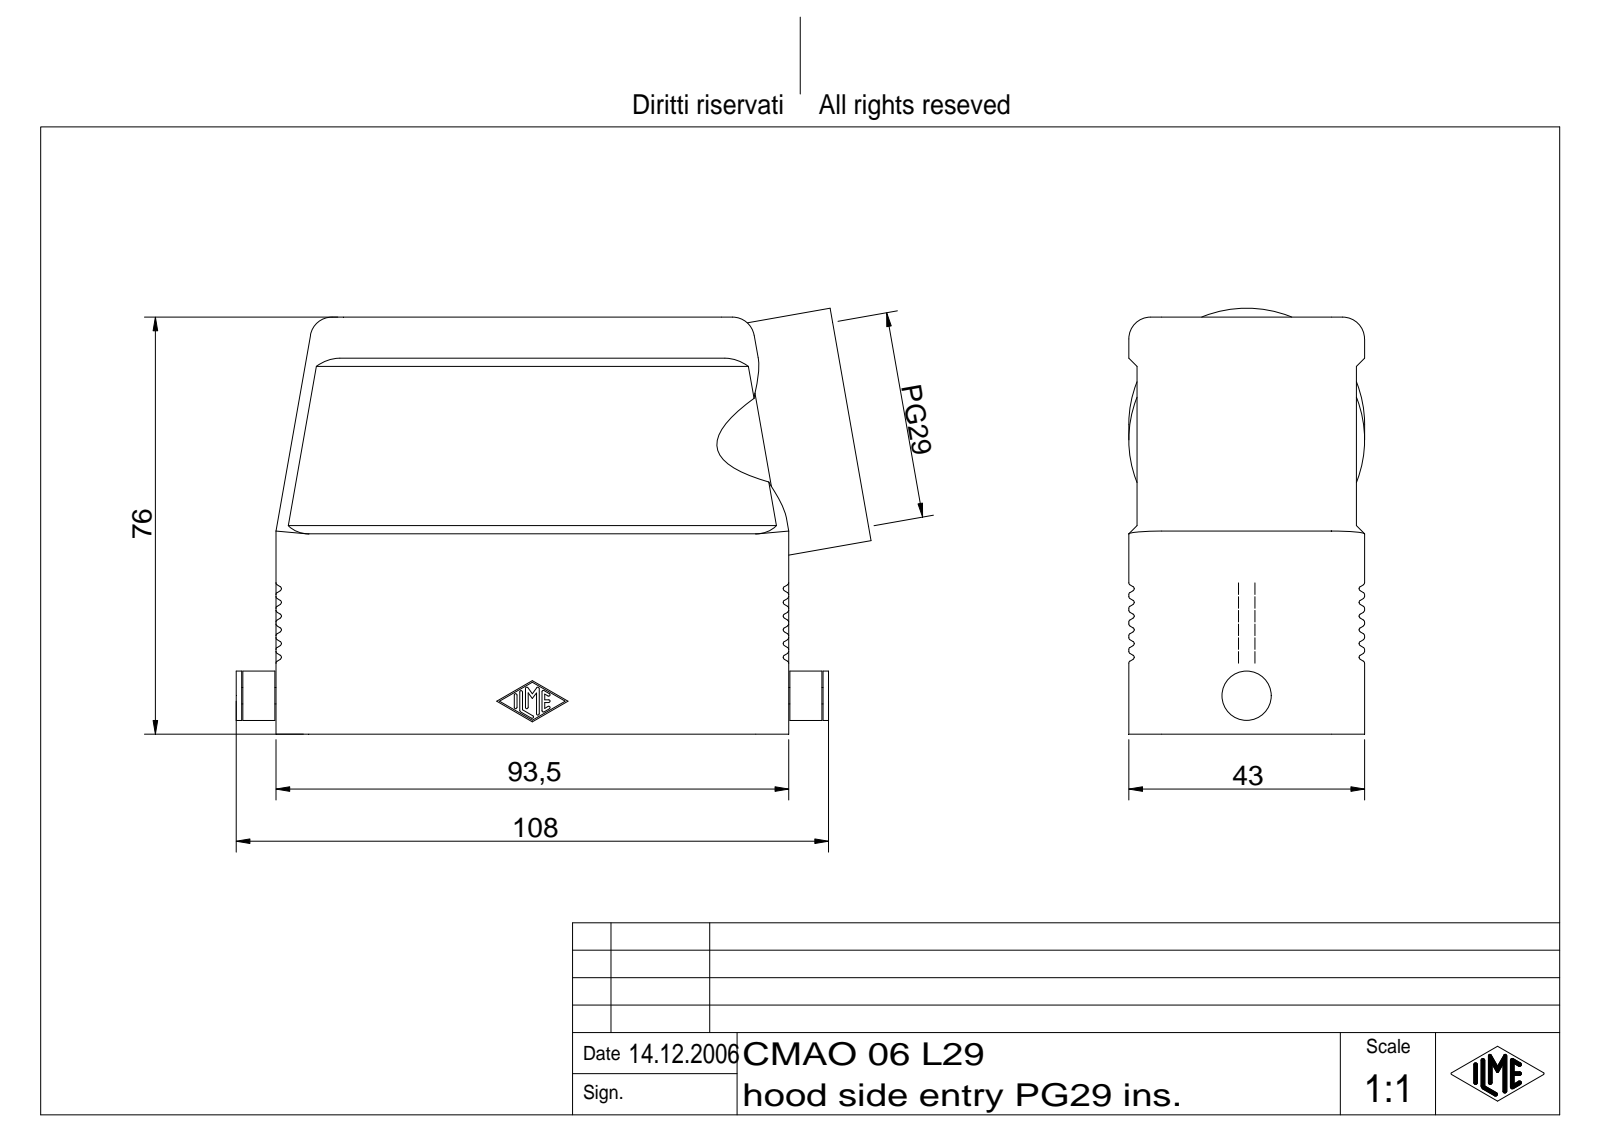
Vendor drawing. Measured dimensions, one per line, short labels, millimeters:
name: CMAO 06 L29
written by: Autodesk Inventor 7 (AUTOMOTIVE_DESIGN)
unit: mm
bodies: 1 solid, 857 faces (154 planar, 424 cylindrical, 279 other)
size: 115.77 × 77.61 × 43
volume: 72 830 mm³; area: 49 174 mm²
holes: 1× ⌀33.7, 1× ⌀35.48
bosses: 1× ⌀43, 1× ⌀9, 1× ⌀3
rounds: 96× R0.4, 14× R0.25, 8× R6, 4× R1.5, 4× R3, 4× R4, 2× R5
face distances: 1.5, 3, 40, 37, 38.5, 41.5, 43, 90.5, 79.25, 82.25
